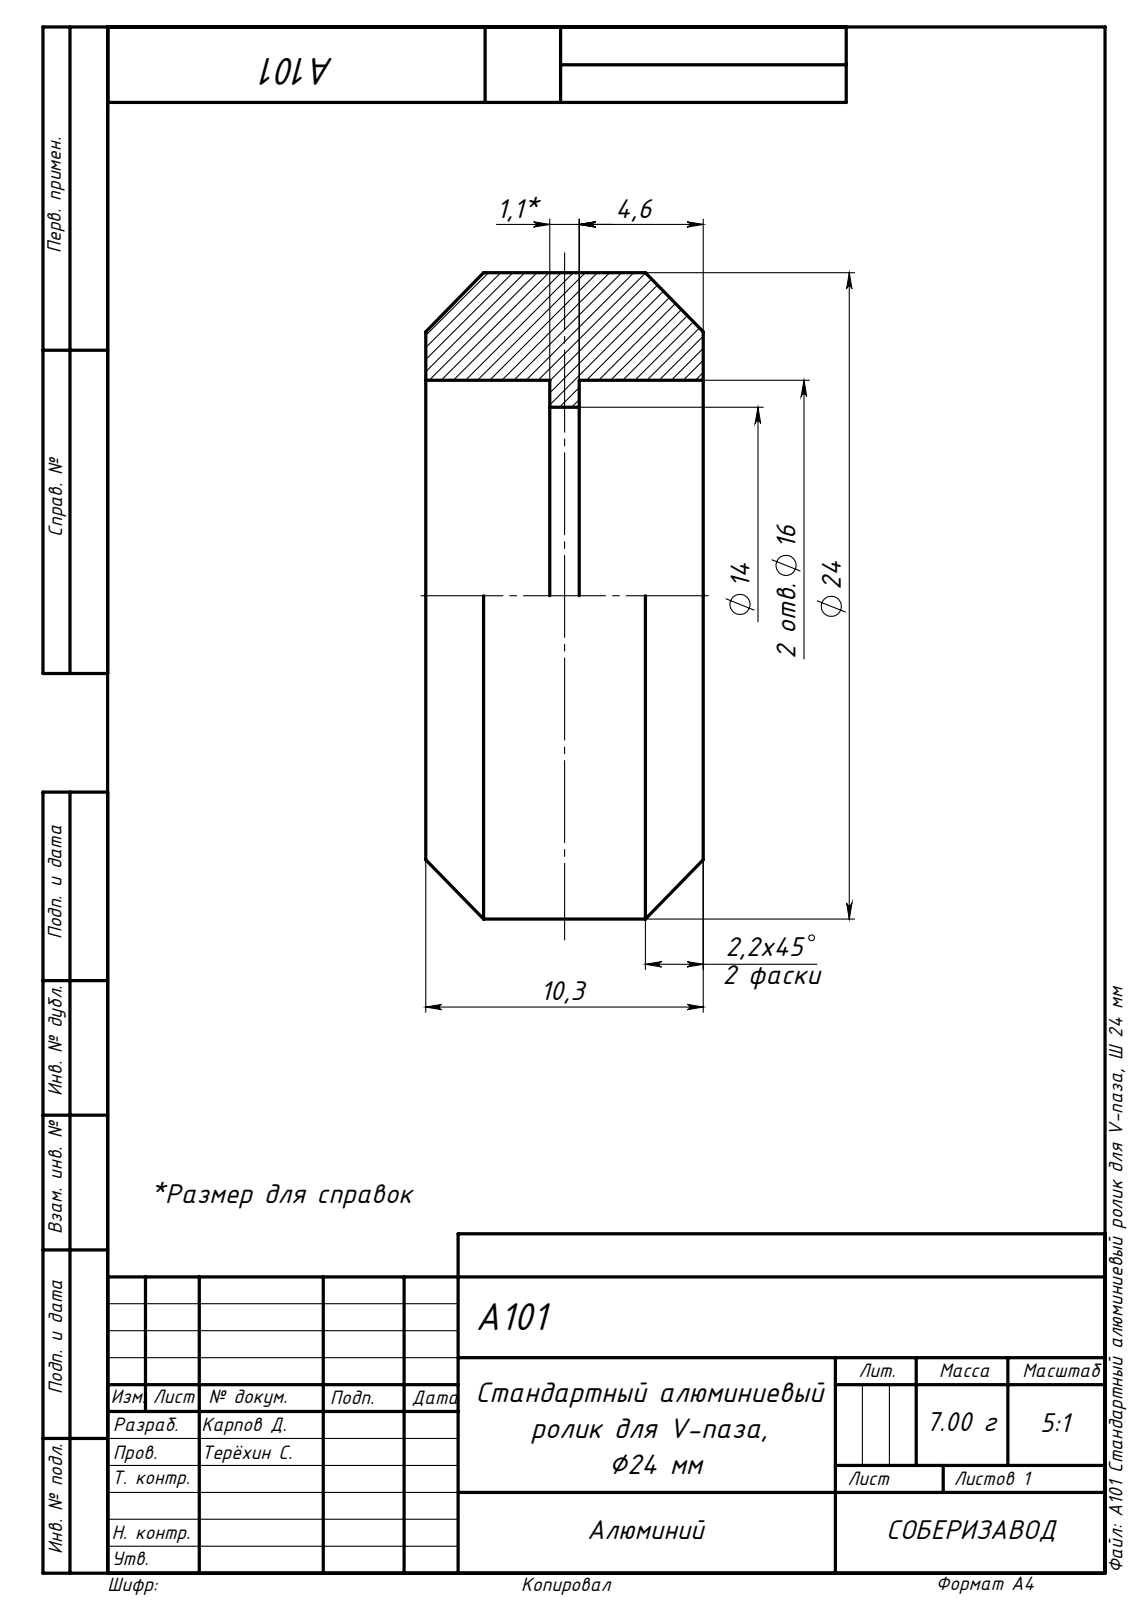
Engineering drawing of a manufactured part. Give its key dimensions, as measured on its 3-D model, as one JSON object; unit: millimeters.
{"step_written_by": "SolidWorks 2019 (AUTOMOTIVE_DESIGN)", "units": "millimeters", "bodies": {"solids": 1, "faces": 16, "planar": 4, "cylindrical": 8, "other": 4}, "overall_size": [24, 24, 10.3], "volume_mm3": 2306, "surface_area_mm2": 1680, "round_holes": [[14, 1], [16, 1]], "round_bosses_or_shafts": [[24, 1]], "face_to_face_distances": [10.3, 4.6, 5.7, 1.1]}
